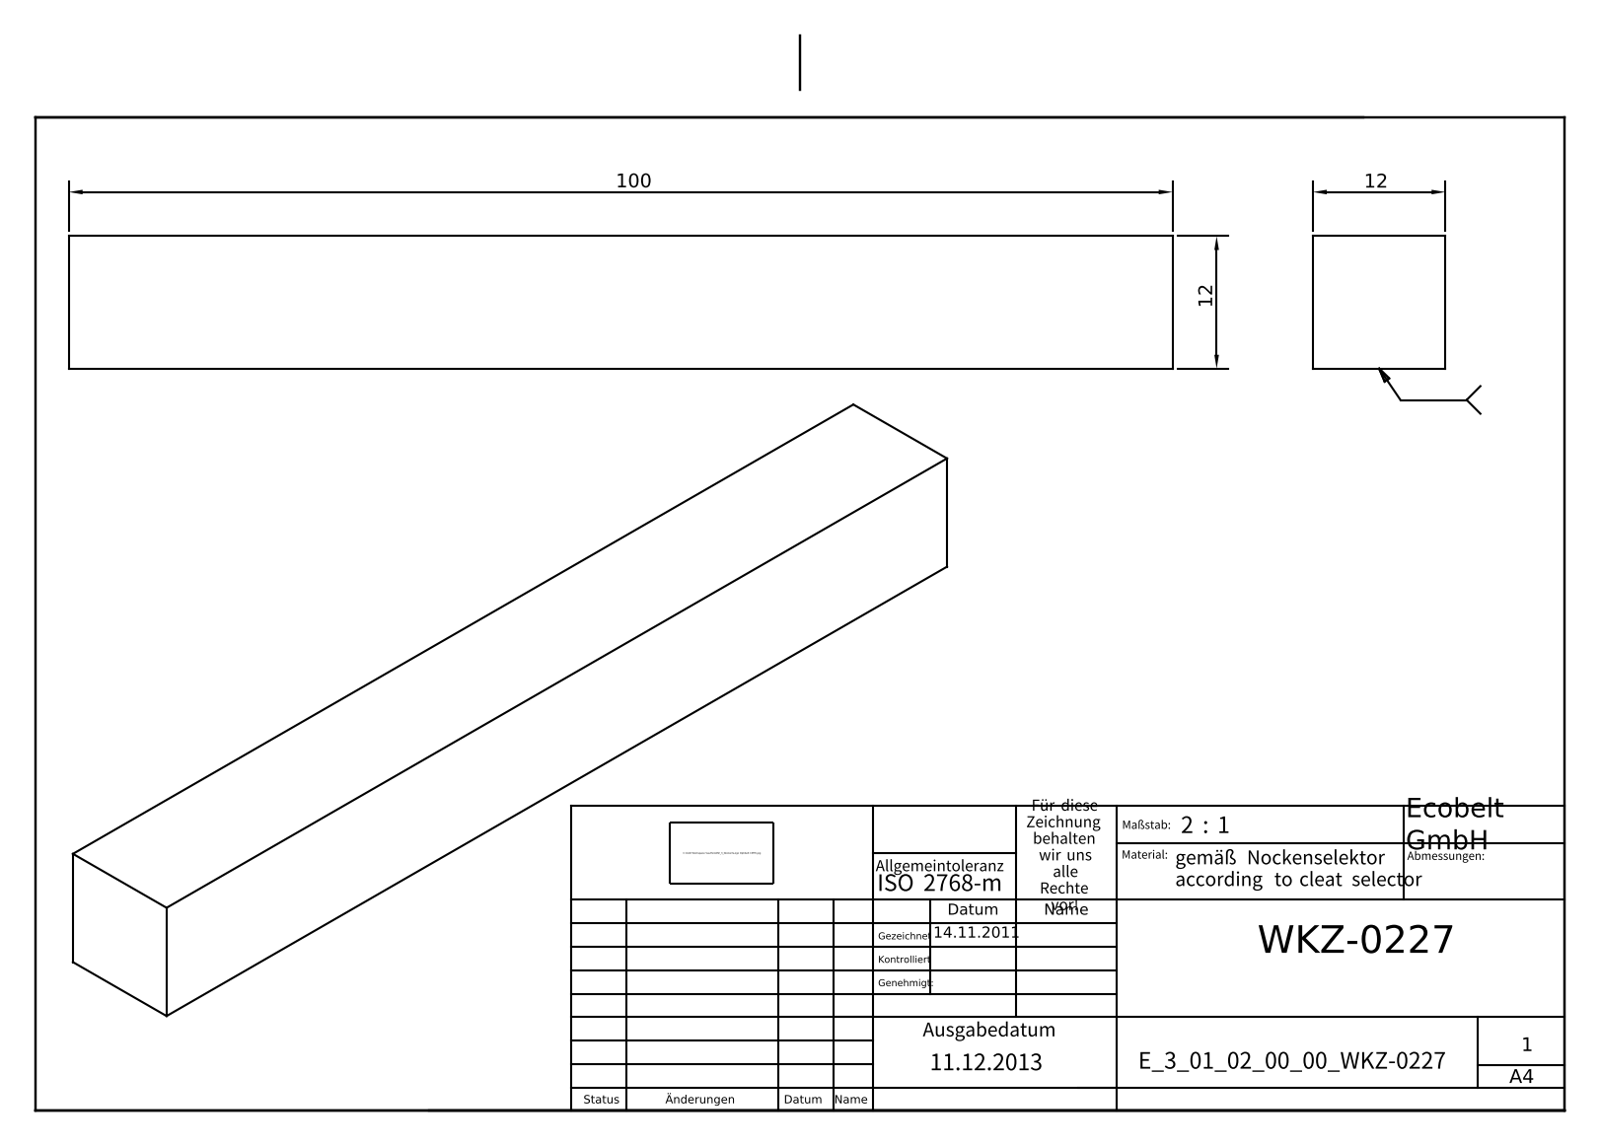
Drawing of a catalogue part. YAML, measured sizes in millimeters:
part_name: "E_3_01_02_00_00_WKZ-0227"
step_written_by: "Autodesk Inventor 2021 (AUTOMOTIVE_DESIGN)"
units: millimeters
bodies: {solids: 1, faces: 6, planar: 6, cylindrical: 0, other: 0}
overall_size: [100, 12, 12]
volume: 14400
surface_area: 5088
face_to_face_distances: [12, 100]
